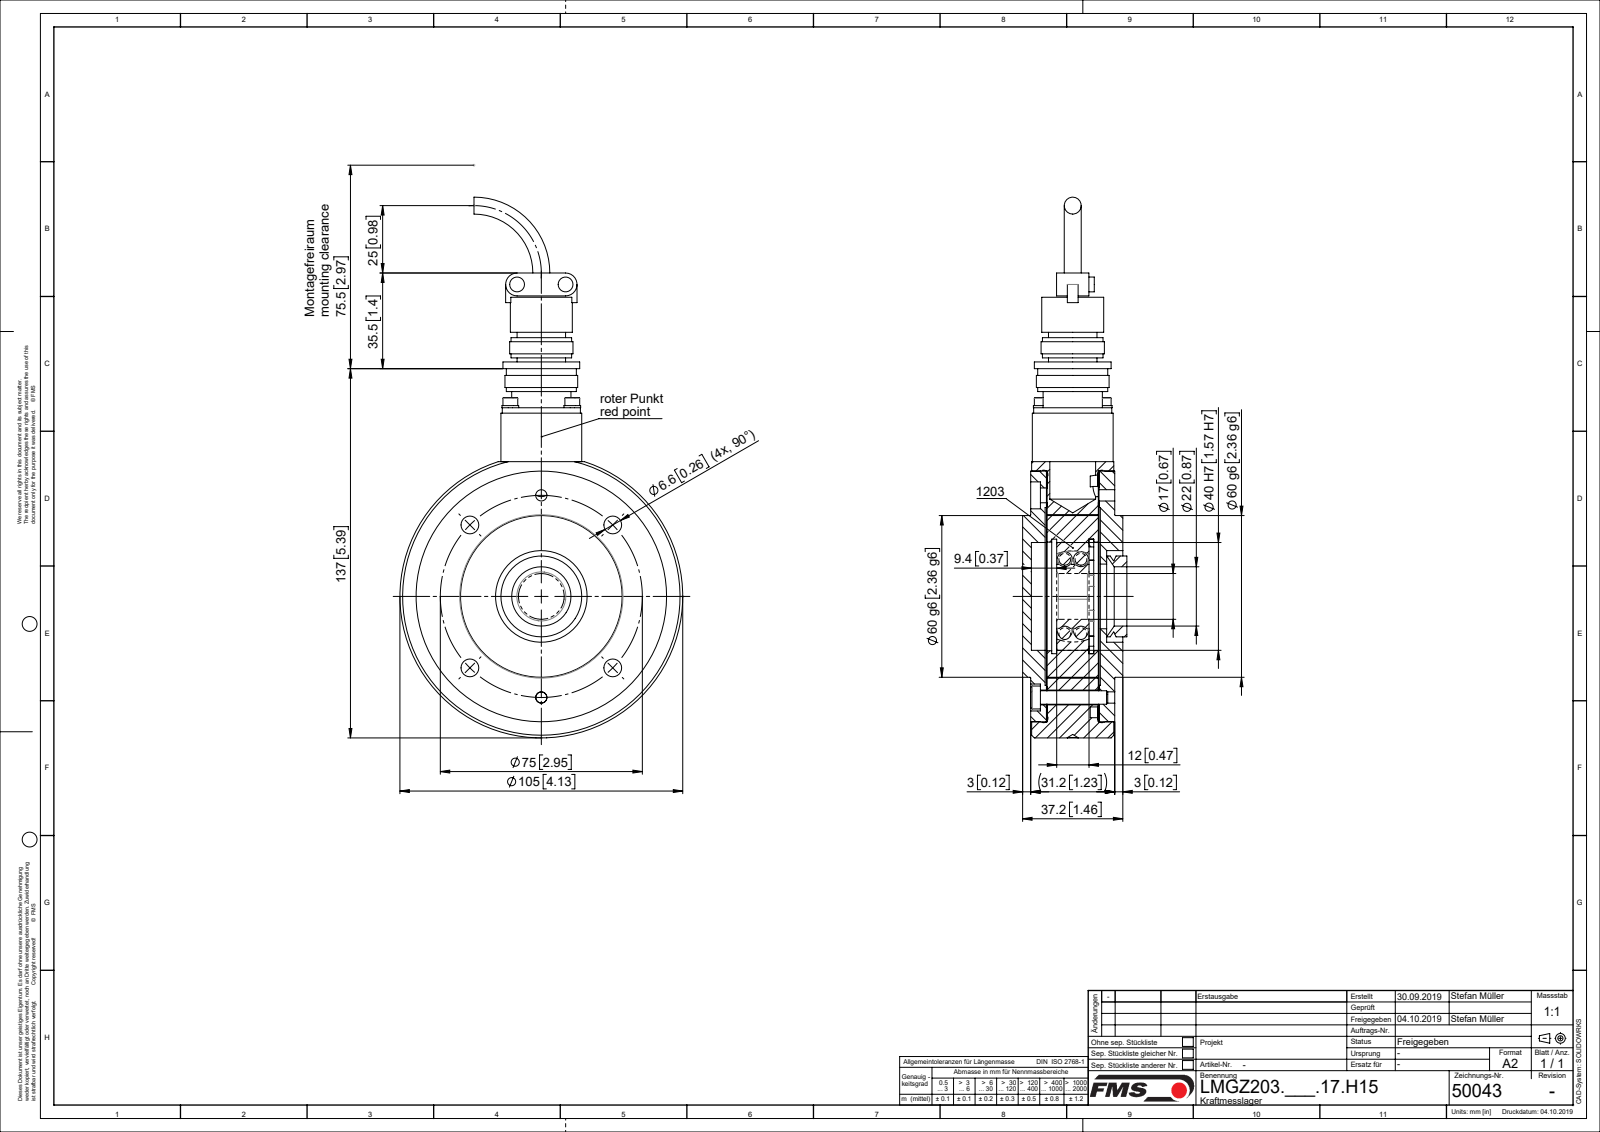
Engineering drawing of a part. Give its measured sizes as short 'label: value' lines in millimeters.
name: L50043; L4936404; TEIL1; L47958 (+8 more)
written by: Mechanical Desktop 2007 (CONFIG_CONTROL_DESIGN)
unit: mm
bodies: 19 solids, 361 faces (104 planar, 219 cylindrical, 38 other)
size: 200.65 × 105 × 37.2
volume: 286 182 mm³; area: 103 042 mm²
holes: 4× ⌀2.6, 4× ⌀3.2, 4× ⌀3.4, 4× ⌀6.6, 2× ⌀4, 2× ⌀5.3, 2× ⌀5.5, 2× ⌀10, 1× ⌀17, 1× ⌀22, 1× ⌀23, 1× ⌀24
bosses: 6× ⌀5.5, 4× ⌀6.2, 4× ⌀3, 4× ⌀2.5, 1× ⌀105, 1× ⌀93, 1× ⌀60, 1× ⌀30
rounds: 2× R4.25
face distances: 19.25, 19, 5.85, 25.1, 6.1, 25.35, 19.5, 20, 3, 0.5
hole spacings: 37.5, 16.26, 23, 28.7, 53.04, 69.3, 32.53, 75.01
